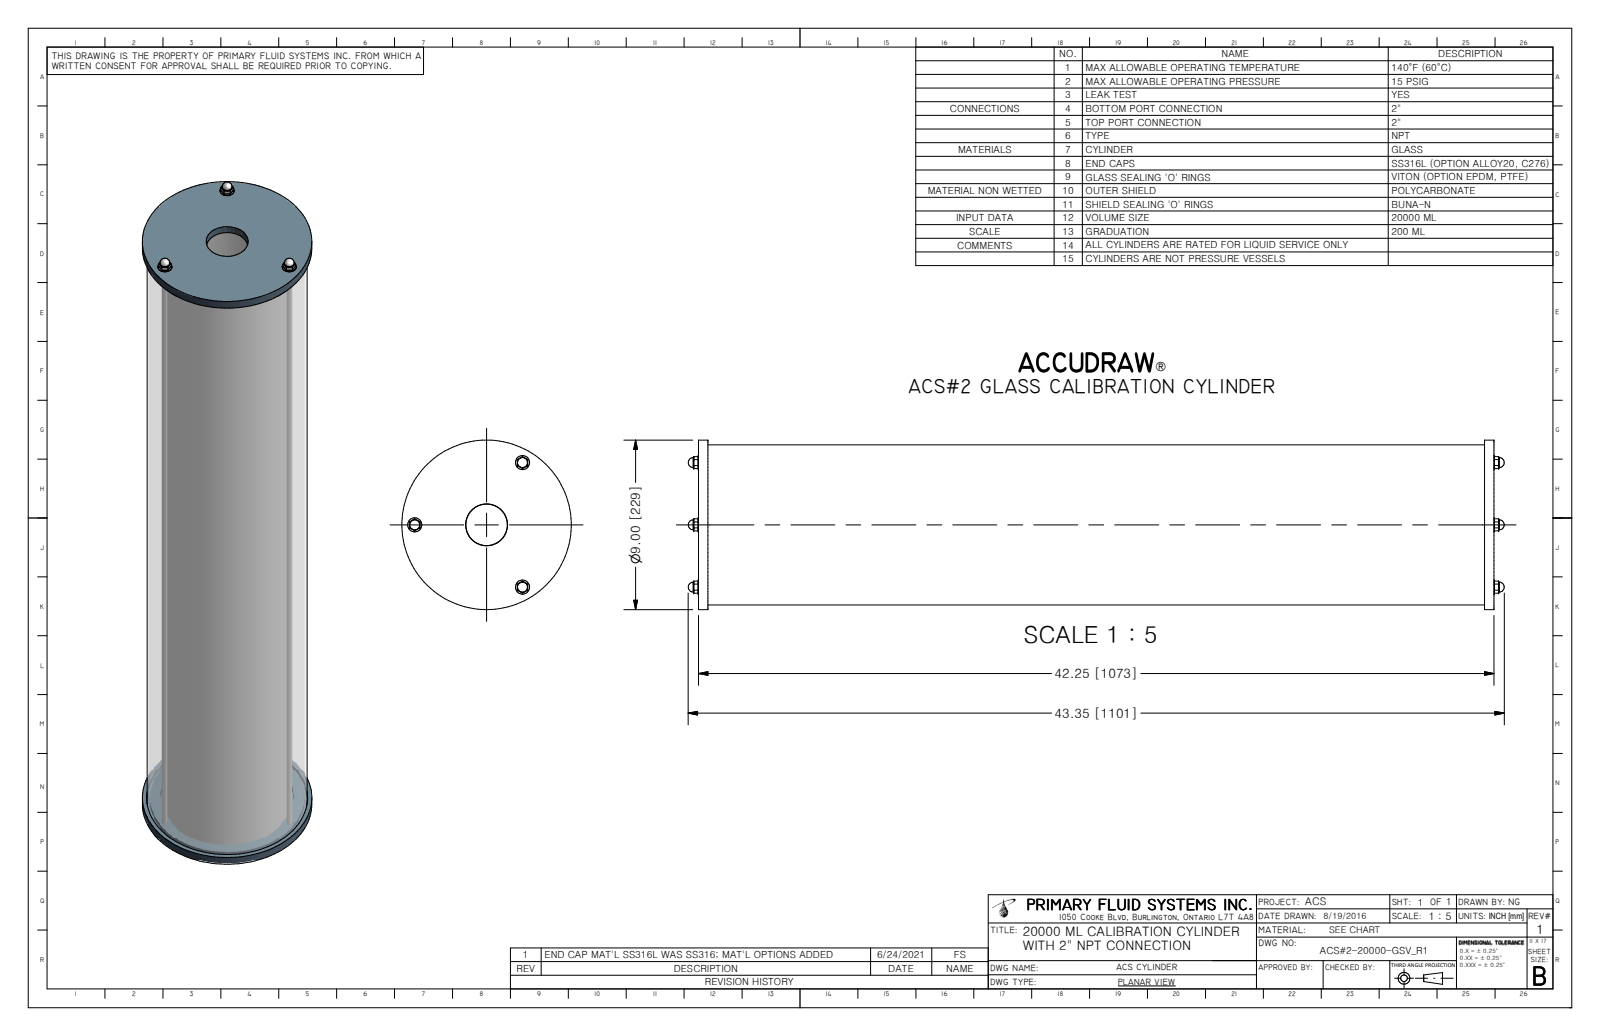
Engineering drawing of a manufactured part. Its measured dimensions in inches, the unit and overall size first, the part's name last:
Units: inches
Overall size (bounding box): 43.35 × 9 × 9
Round holes (diameter × count): ⌀0.328 ×3, ⌀0.344 ×3, ⌀6.252 ×1, ⌀7.125 ×1, ⌀8.25 ×1, ⌀8.55 ×1
Round bosses / shafts (diameter × count): ⌀0.75 ×3, ⌀0.528 ×3, ⌀0.313 ×3, ⌀9 ×1, ⌀8.5 ×1, ⌀8.2 ×1, ⌀6.804 ×1, ⌀6.165 ×1
Partial cylindrical surfaces — rounded edges, fillets, slot ends (radius × count): R0.005 ×56
Main face-to-face distances: 42.25, 0.5, 41.75, 0.375, 42.125, 0.125, 41.625, 41.25, 42, 0.225
Hole centre spacings: 3.817, 6.611, 6.611
Volume: 431.5 in³ · Surface area: 4 399 in²
Bodies: 19 solids, 215 faces (80 planar, 113 cylindrical, 22 other)
Part name (STEP PRODUCT): ACS#2-20000-GSV_R0; ACS-3-20000-METAL_R3; ACS-2-20000_R6; ACS-1-20000-A_R0 (+3 more)
STEP written by: Autodesk Inventor 2009 (AUTOMOTIVE_DESIGN)
